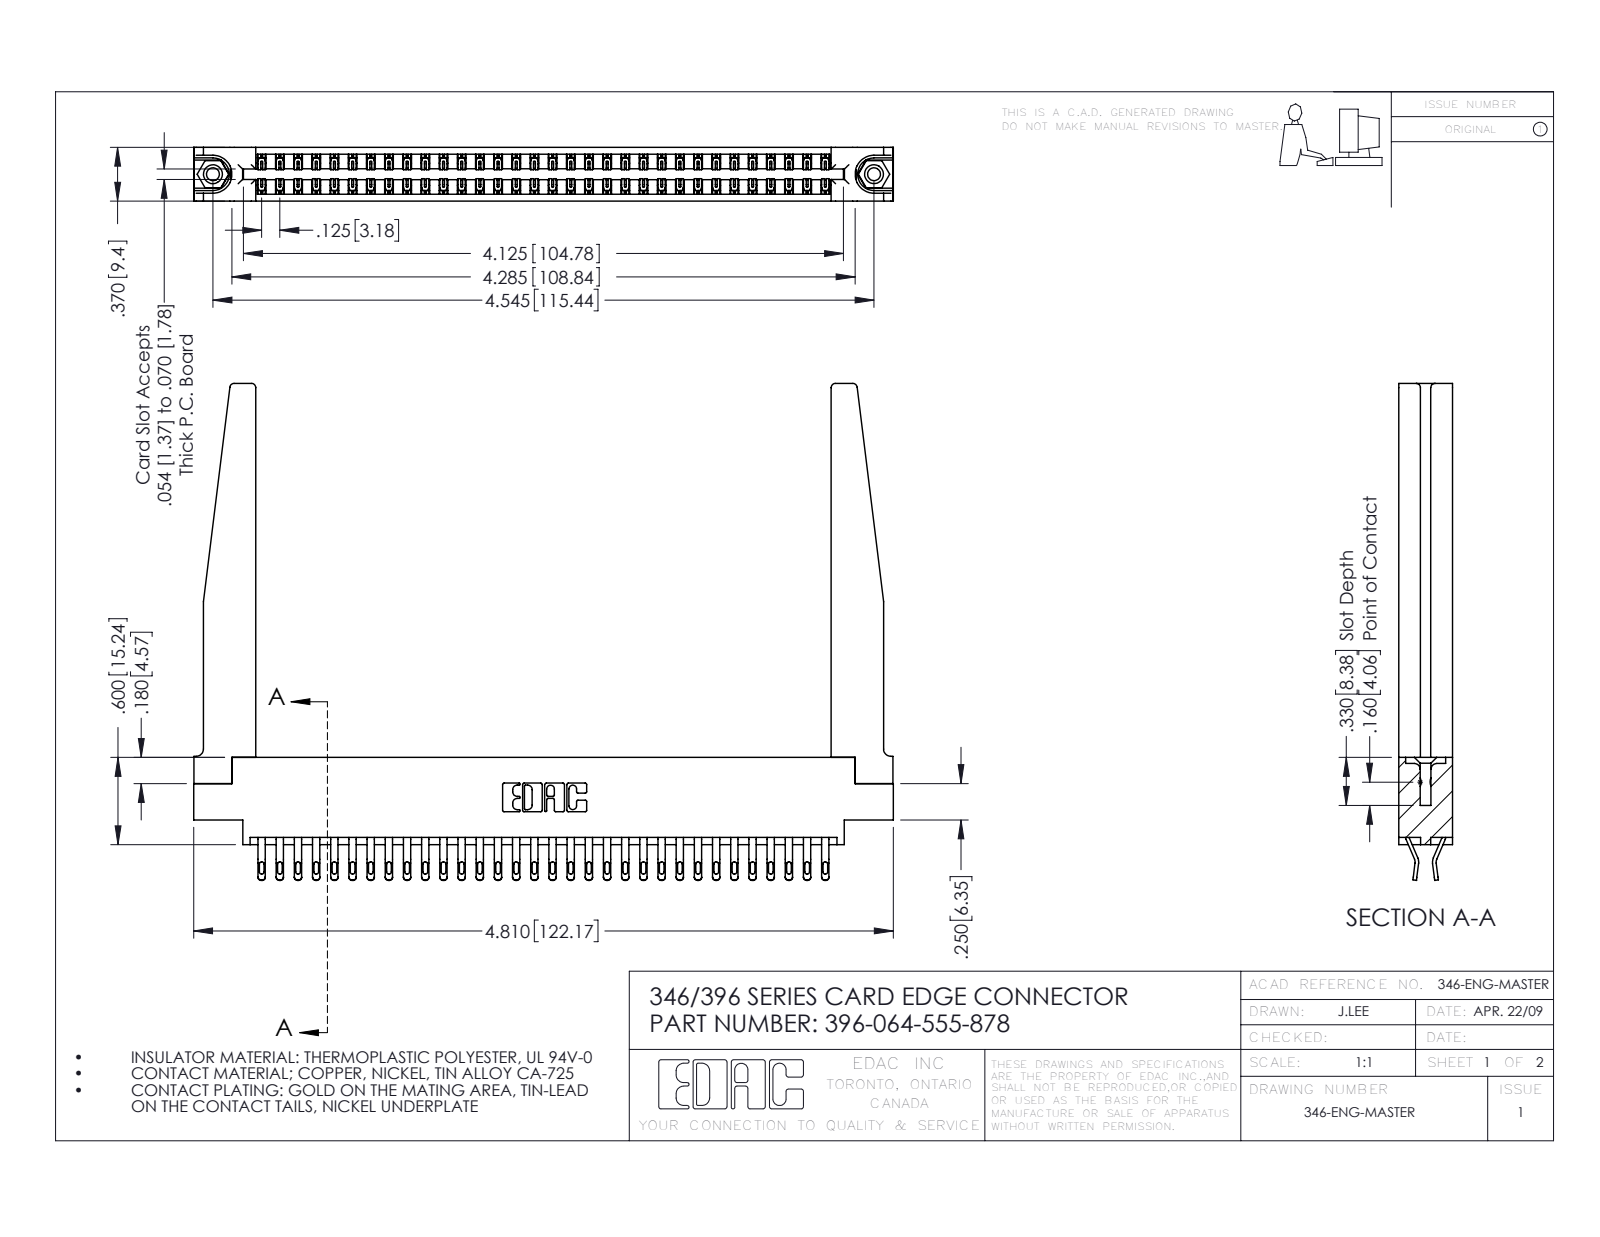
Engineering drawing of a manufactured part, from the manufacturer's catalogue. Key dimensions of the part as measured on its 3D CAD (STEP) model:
Part name (STEP PRODUCT): 396-064-555-878; 346-220-078_345-220-078; 346 Part_0.170 Offset - 0.156 Dia-TH; 345-292-001_555 Tail (+1 more)
STEP written by: SolidWorks 2016 (CONFIG_CONTROL_DESIGN)
Units: inches
Bodies: 69 solids, 4072 faces (2334 planar, 1686 cylindrical, 52 other)
Overall size (bounding box): 4.81 × 3.415 × 0.37
Volume: 1.146 in³ · Surface area: 36.48 in²
Round holes (diameter × count): ⌀0.089 ×2, ⌀0.125 ×2, ⌀0.156 ×2, ⌀0.064 ×1
Round bosses / shafts (diameter × count): ⌀0.155 ×2
Partial cylindrical surfaces — rounded edges, fillets, slot ends (radius × count): R0.016 ×128, R0.02 ×128, R0.006 ×96, R0.01 ×22, R0.03 ×8, R0.007 ×6, R0.031 ×6, R0.05 ×4
Main face-to-face distances: 0.37, 0.048, 0.322, 0.072, 0.148, 0.15, 0.25, 0.025, 0.298, 0.275
Hole centre spacings: 0.246, 4.337, 4.545
